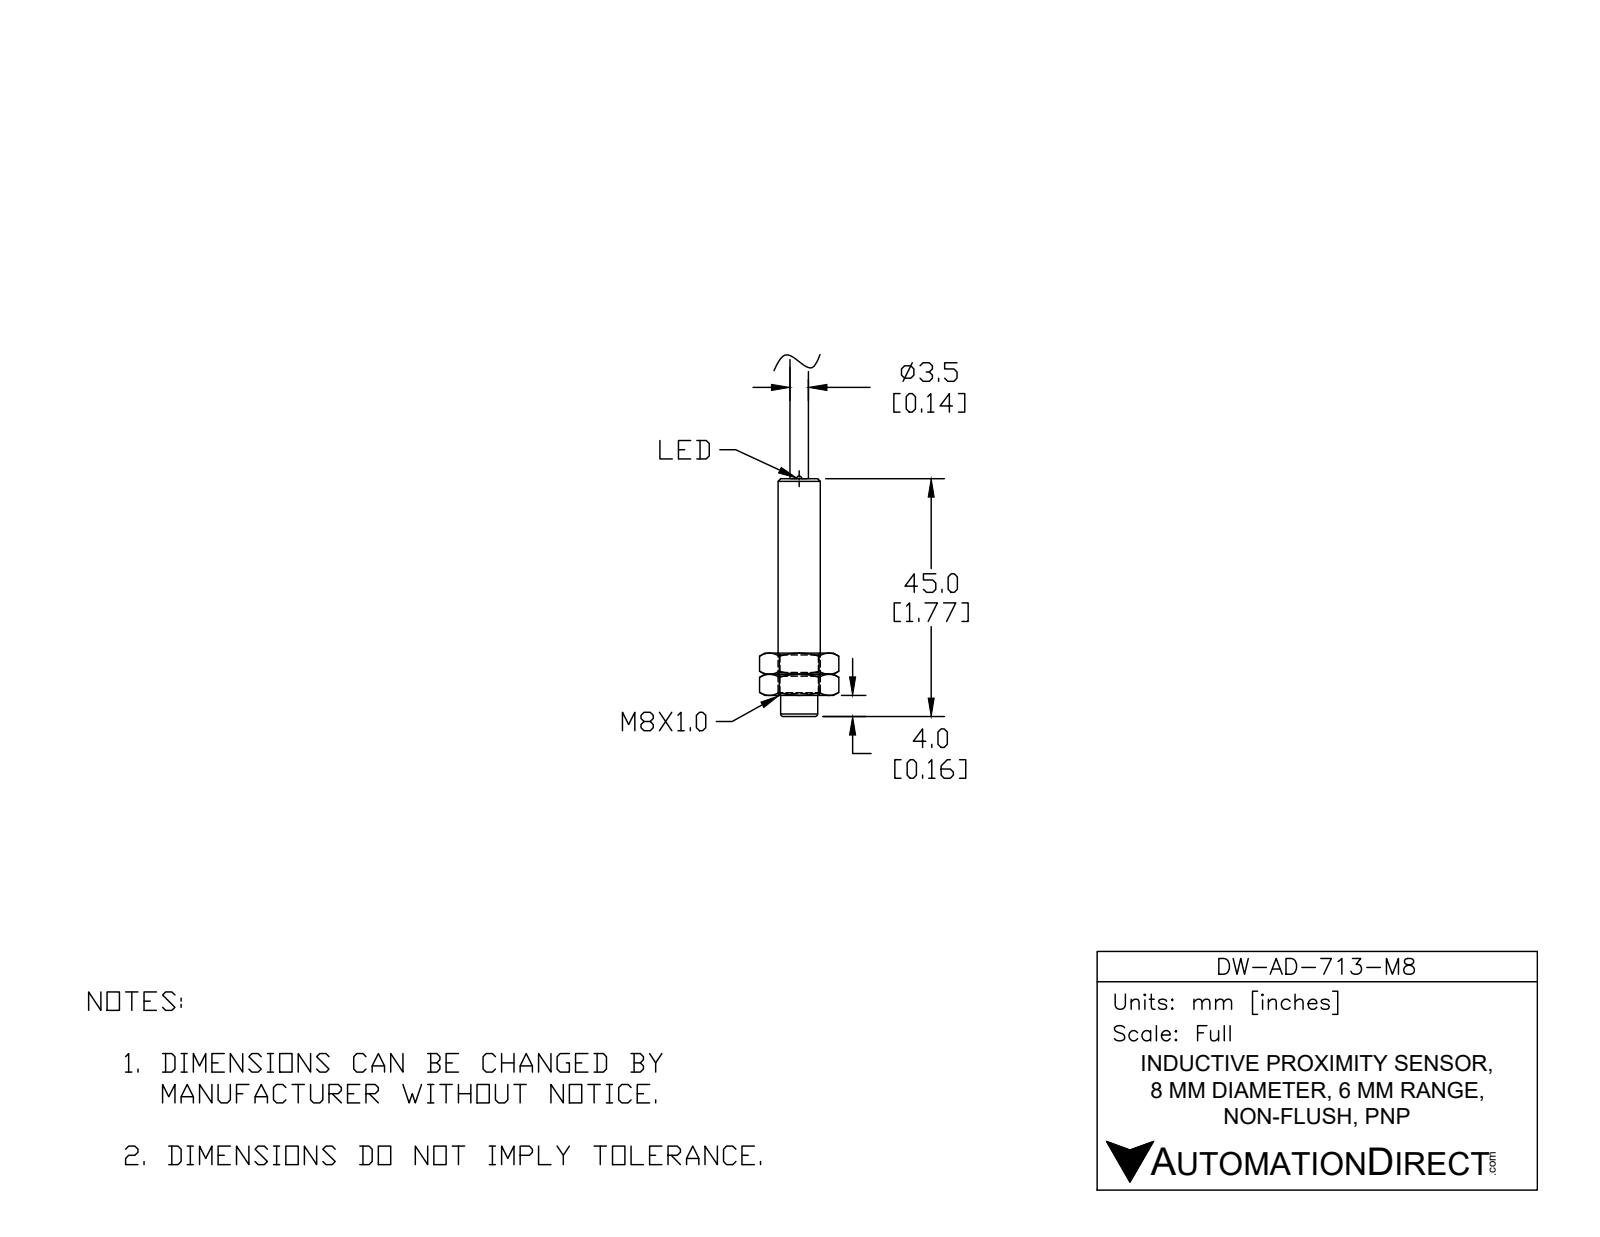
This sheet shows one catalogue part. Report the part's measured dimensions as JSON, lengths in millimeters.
{"part_name": "DW-AD-713-M8", "step_written_by": "SolidWorks 2017 (AUTOMOTIVE_DESIGN)", "units": "millimeters", "bodies": {"solids": 2, "faces": 9, "planar": 4, "cylindrical": 3, "other": 2}, "overall_size": [65, 8, 8], "volume_mm3": 2410, "surface_area_mm2": 1443, "round_bosses_or_shafts": [[8, 1], [7, 1], [3.5, 1]], "face_to_face_distances": [45, 20, 65]}
